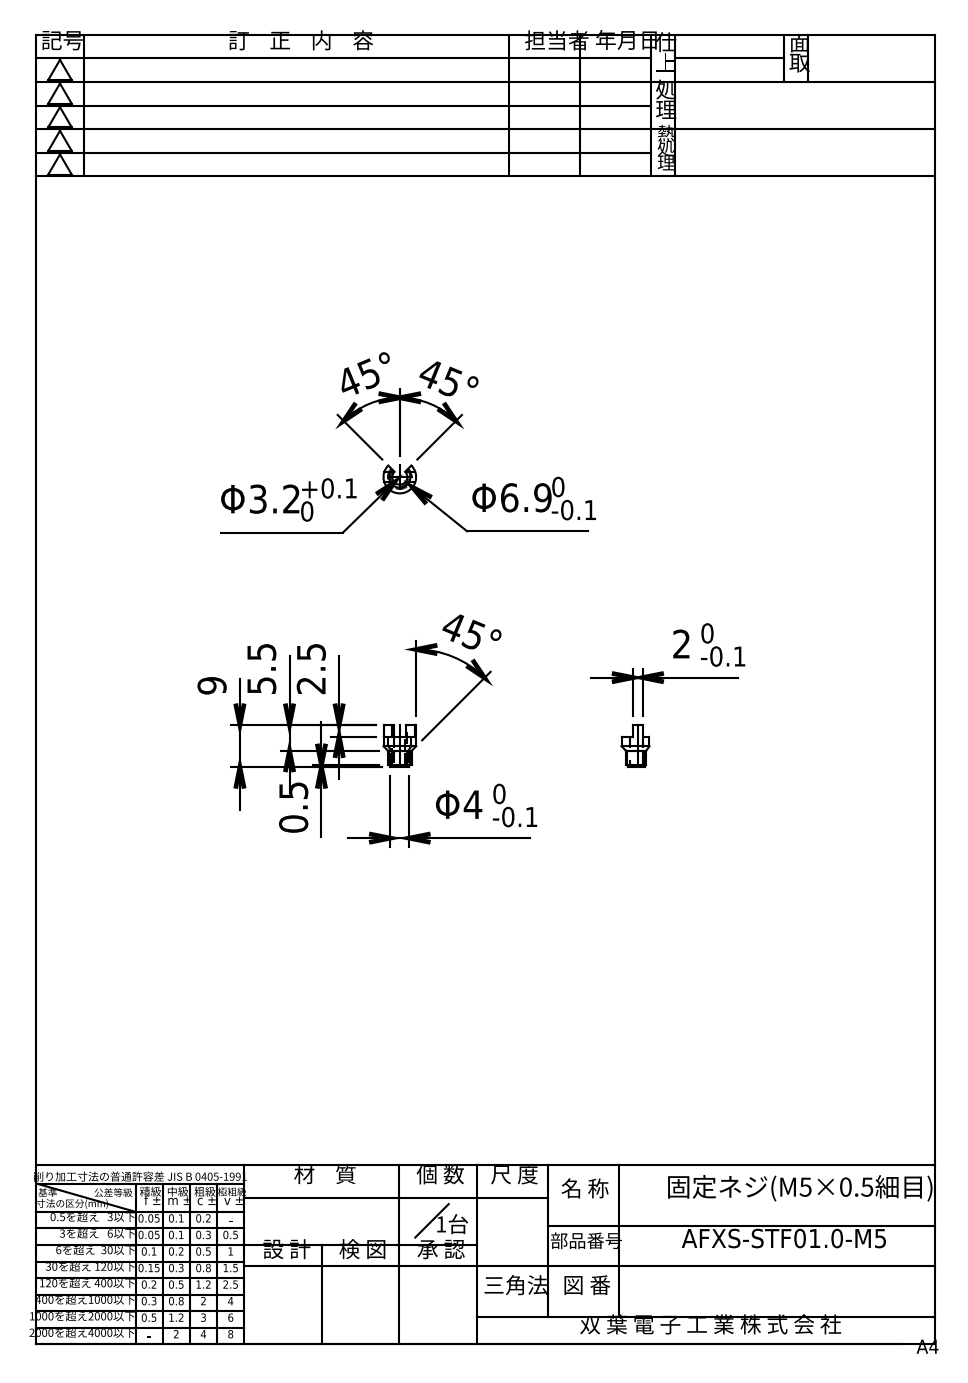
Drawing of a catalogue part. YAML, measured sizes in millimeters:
step_written_by: "XStep 1.0 (automotive_design)"
units: millimeters
bodies: {solids: 1, faces: 18, planar: 13, cylindrical: 4, other: 1}
overall_size: [9, 6.9, 5.89]
volume: 106
surface_area: 229
partial_cylinders:
  - {radius: 1.6, count: 1}
  - {radius: 2, count: 1}
  - {radius: 2.5, count: 1}
  - {radius: 3.45, count: 1}
face_to_face_distances: [2, 2.5, 6, 8.5, 0.5, 6.5, 9]
